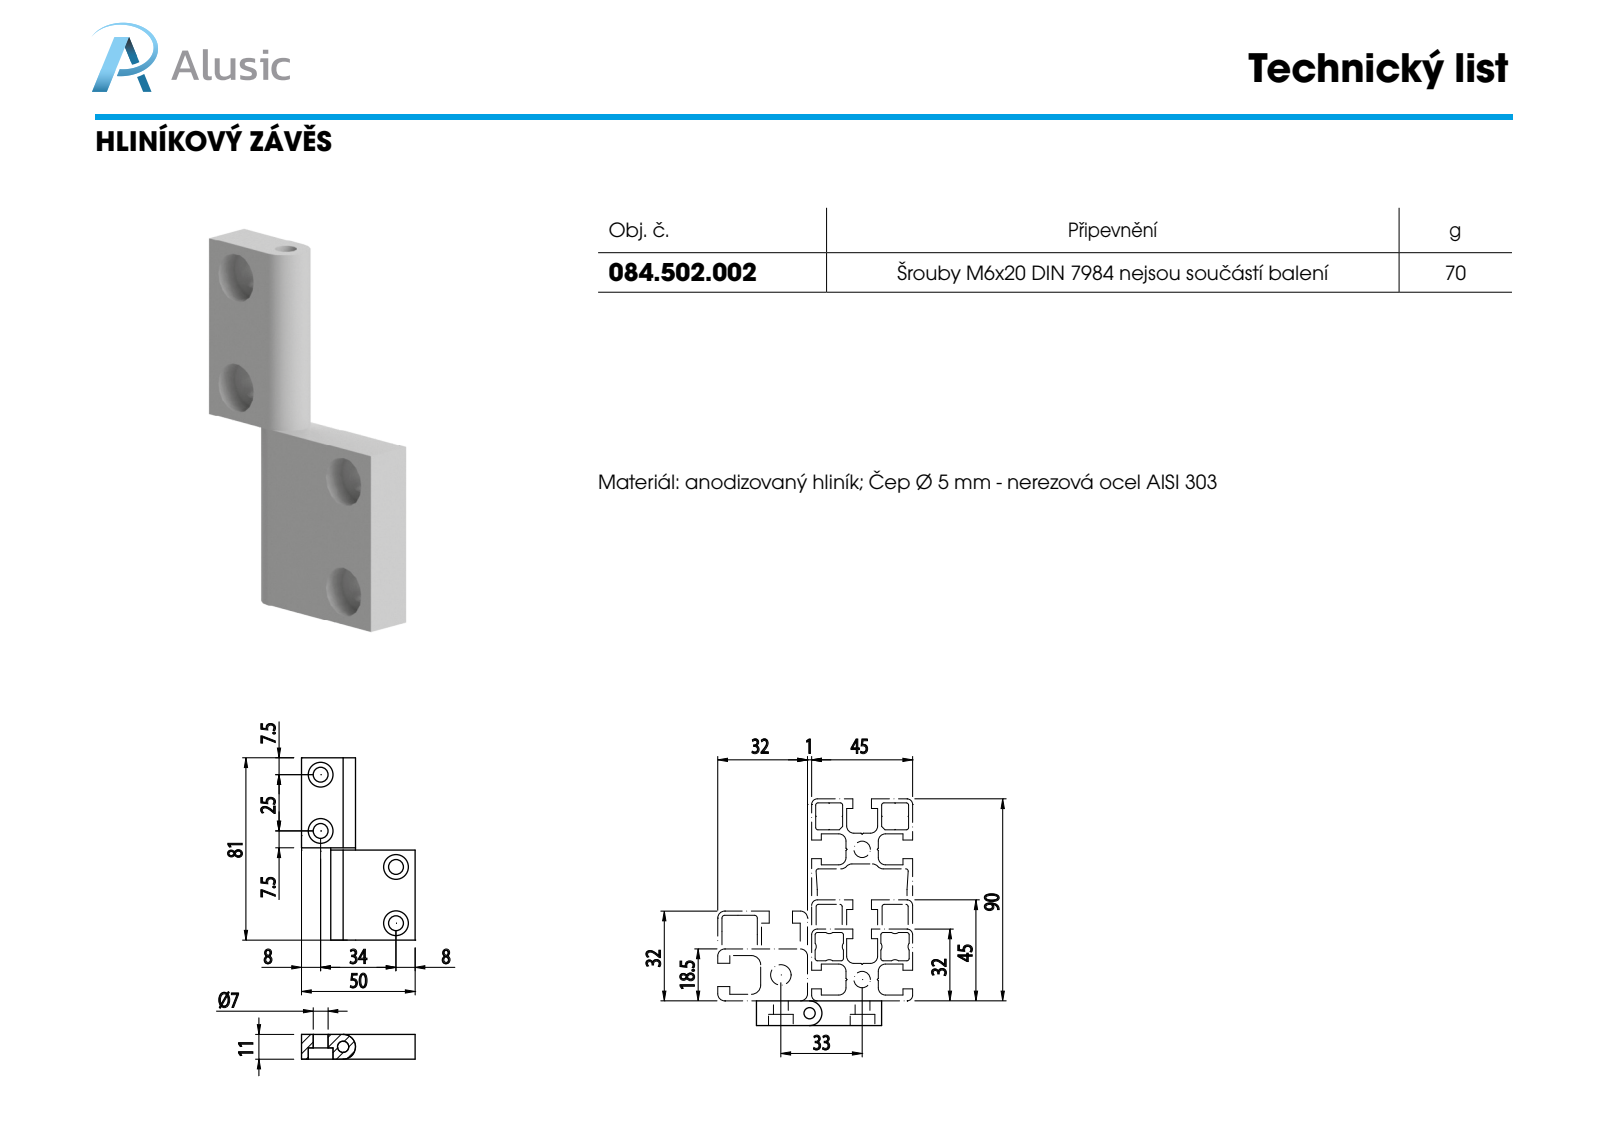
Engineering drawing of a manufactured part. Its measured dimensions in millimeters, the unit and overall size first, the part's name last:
Units: millimetres
Overall size (bounding box): 80 × 50.5 × 11
Round holes (diameter × count): ⌀6.6 ×4, ⌀11 ×4, ⌀5 ×1
Round bosses / shafts (diameter × count): ⌀11 ×1
Main face-to-face distances: 11, 40, 50.5, 6, 5, 80
Hole centre spacings: 25, 52.18, 36.7, 73.12
Volume: 21 729 mm³ · Surface area: 9 697 mm²
Bodies: 2 solids, 36 faces (14 planar, 22 cylindrical, 0 other)
Part name (STEP PRODUCT): 084.502.002; 084.502.000 ALETTE_ALETTA 2; 084.502.000 ALETTE_ALETTA 1
STEP written by: SolidWorks 2012 (CONFIG_CONTROL_DESIGN)
